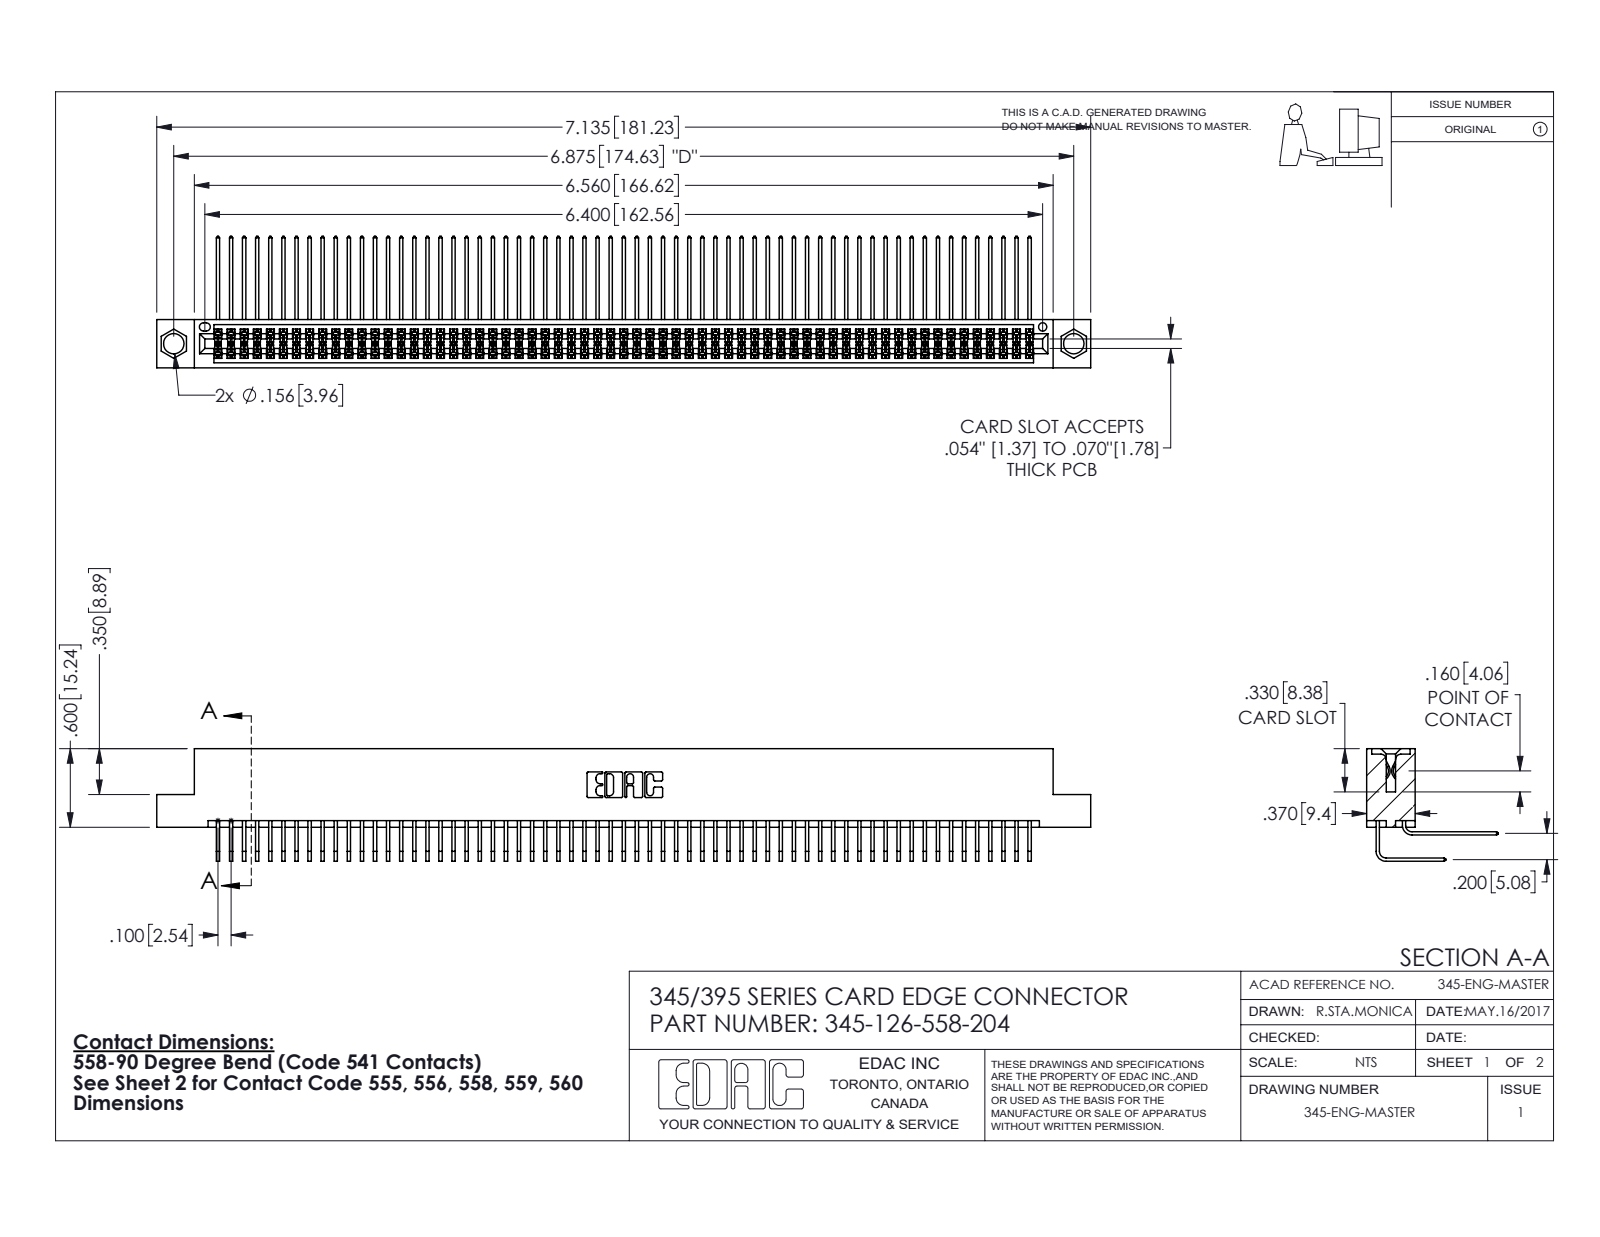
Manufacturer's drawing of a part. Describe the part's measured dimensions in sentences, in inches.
The part is named "345-292-001_558 559 Tail - 1; 345 Part_Flush Mounting Lugs - 0.156 Dia-TI; 345-126-558-204; 345-292-001_558 Tail - 2". Its 3-D file was written by "SolidWorks 2020 (CONFIG_CONTROL_DESIGN)". It is 127 solids with 6692 faces: 4504 planar, 2188 cylindrical and 0 other. Overall it measures 7.135 by 1.005 by 0.859 inches. Its volume is 1.124 cubic inches and its surface area 47.9 square inches. Round holes: 2 of diameter 0.156, 1 of diameter 0.064. Partial cylindrical surfaces (rounded edges, fillets, slot ends): 251 of radius 0.006, 22 of radius 0.01, 6 of radius 0.007, 6 of radius 0.031, 3 of radius 0.026, 2 of radius 0.014, 2 of radius 0.019, 2 of radius 0.022. The main face-to-face distances are 0.072, 0.298, 0.2, 0.37, 0.098, 0.272, 0.025, 0.225, 0.025, 0.175. The hole center spacings are 0.27, 6.639, 6.875.
